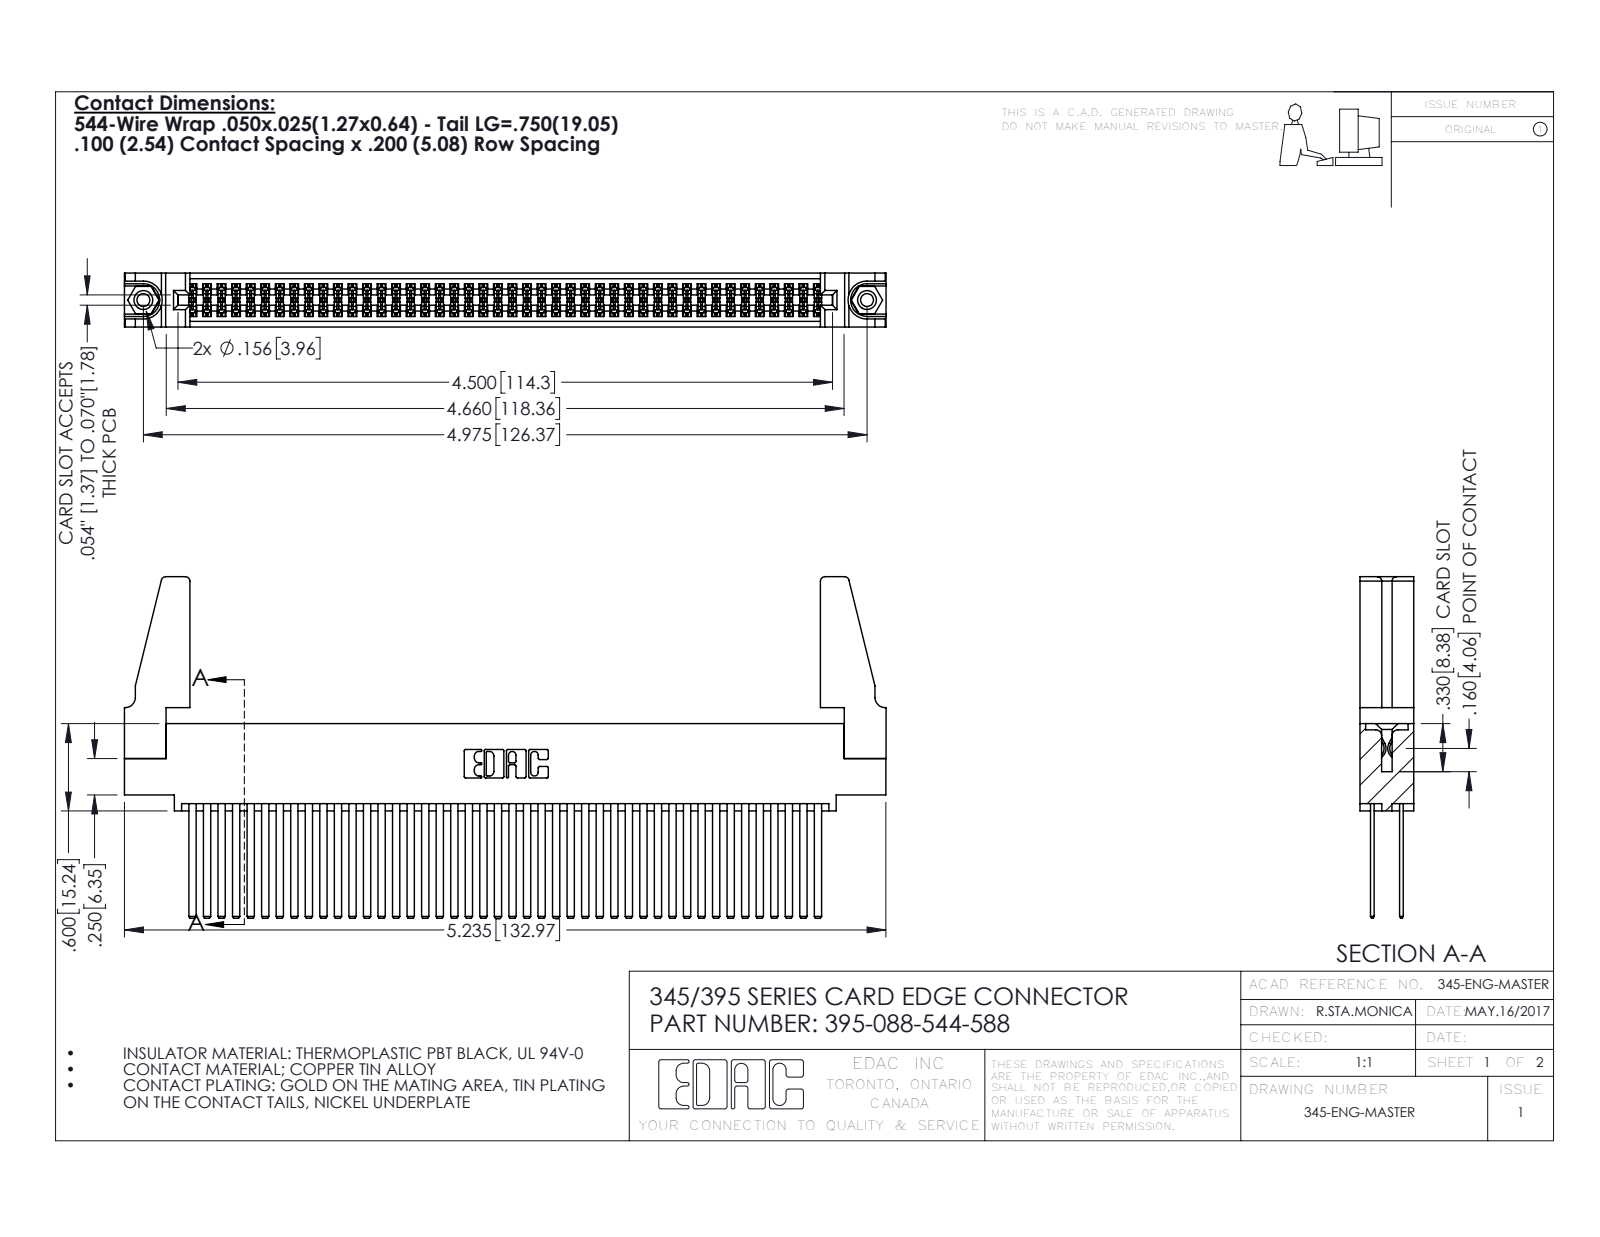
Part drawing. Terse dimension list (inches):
name: 345 Part_0.110 Offset - 0.156 Dia-TH; 345-220-078_345-220-088; 395-088-544-588; 345-250-001_345-250-001-102 (+1 more)
written by: SolidWorks 2016 (CONFIG_CONTROL_DESIGN)
unit: in
bodies: 93 solids, 4126 faces (2708 planar, 1402 cylindrical, 16 other)
size: 5.236 × 2.347 × 0.37
volume: 1.059 in³; area: 42.95 in²
holes: 2× ⌀0.089, 2× ⌀0.125, 2× ⌀0.156, 1× ⌀0.064
bosses: 2× ⌀0.155
rounds: 132× R0.006, 22× R0.01, 8× R0.03, 6× R0.007, 6× R0.031, 3× R0.026, 2× R0.014, 2× R0.019
face distances: 0.072, 0.298, 0.2, 0.098, 0.272, 0.025, 0.225, 0.37, 0.175, 0.149
hole spacings: 0.27, 4.739, 4.975
